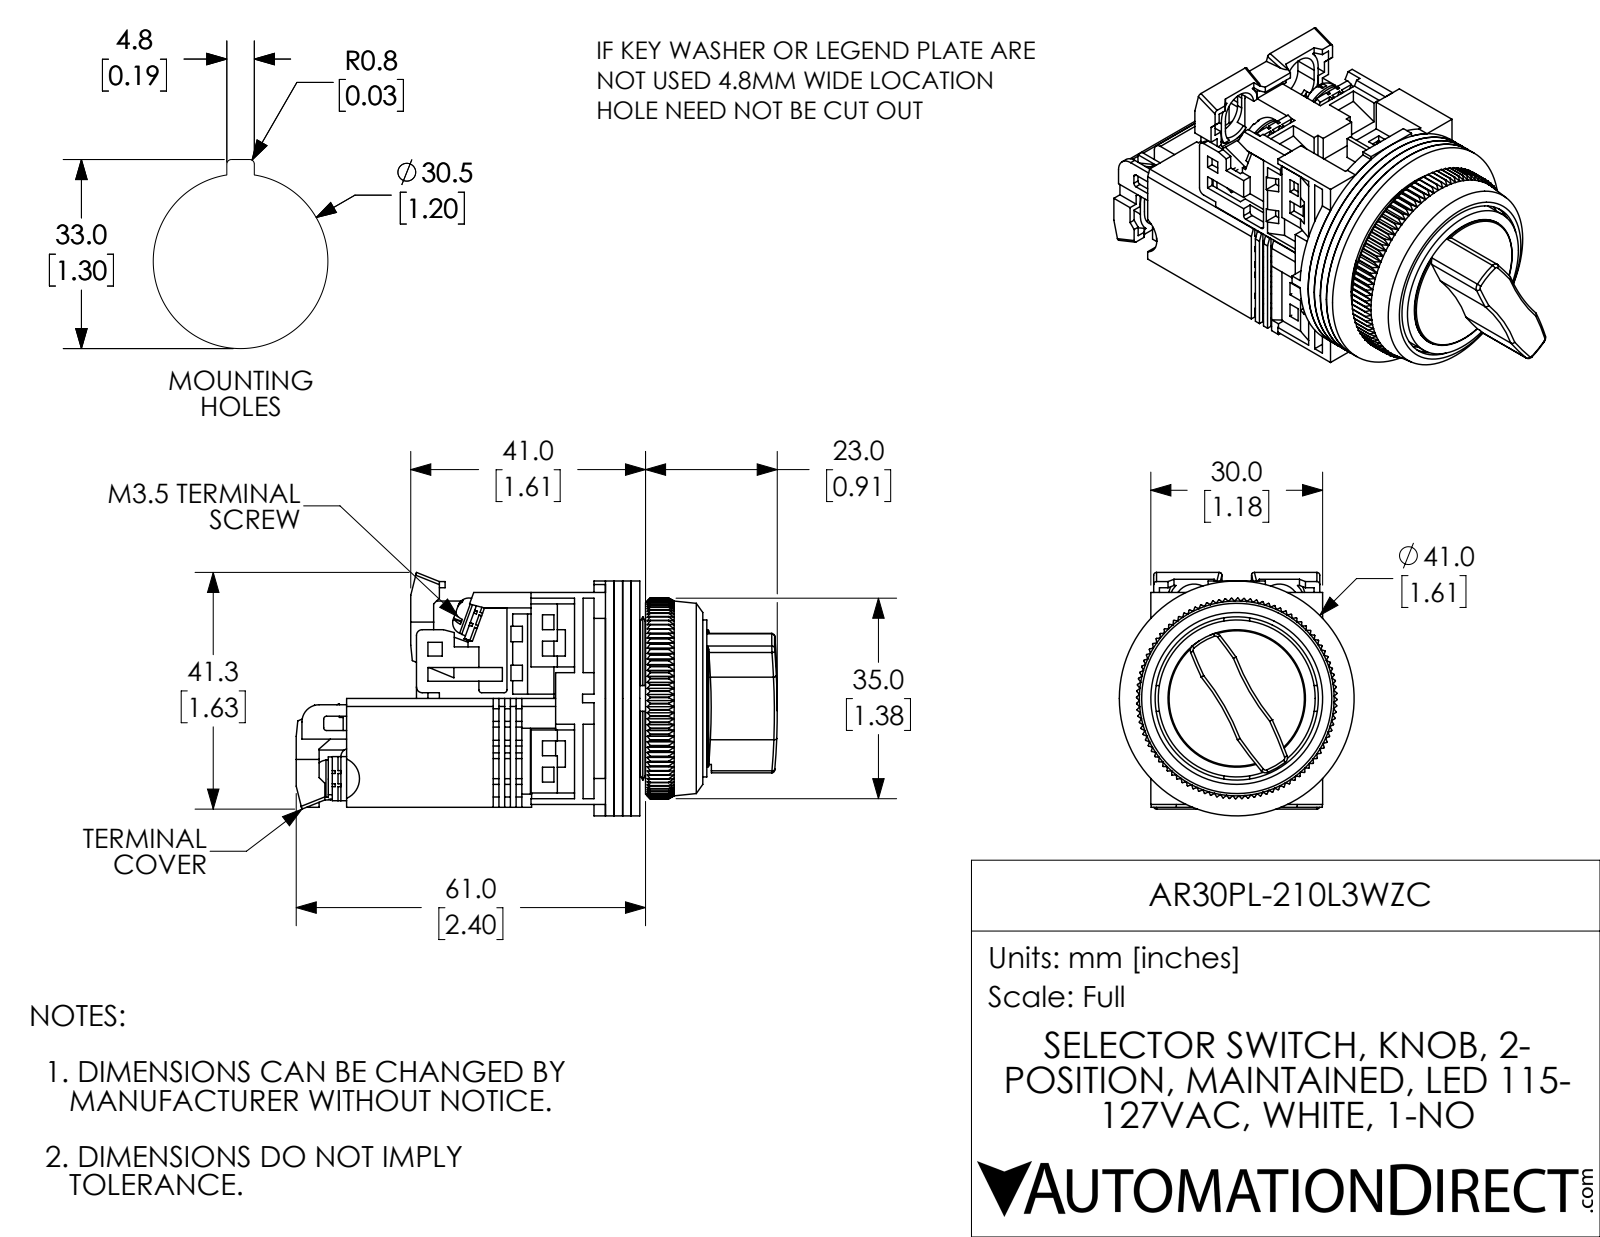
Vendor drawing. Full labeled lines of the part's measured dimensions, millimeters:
Part name (STEP PRODUCT): AR30PL-210L3WZC
STEP written by: SolidWorks 2017 (AUTOMOTIVE_DESIGN)
Units: millimetres
Bodies: 27 solids, 2357 faces (1706 planar, 321 cylindrical, 330 other)
Overall size (bounding box): 84 × 42.5 × 41
Volume: 49 180 mm³ · Surface area: 40 890 mm²
Round holes (diameter × count): ⌀3.5 ×6, ⌀3.6 ×4, ⌀3 ×3, ⌀12 ×1, ⌀18 ×1, ⌀19.5 ×1, ⌀21 ×1, ⌀28.5 ×1, ⌀30 ×1, ⌀31.8 ×1
Round bosses / shafts (diameter × count): ⌀6.6 ×4, ⌀3.5 ×2, ⌀1.6 ×2, ⌀41 ×1, ⌀29.2 ×1, ⌀27.4 ×1, ⌀24 ×1, ⌀22.5 ×1
Partial cylindrical surfaces — rounded edges, fillets, slot ends (radius × count): R1.5 ×17, R0.5 ×13, R1 ×6, R3.5 ×4, R4.5 ×4, R3 ×2, R40 ×2, R75 ×2
Main face-to-face distances: 1.5, 3, 4.5, 2, 1, 19, 20, 5, 6.5, 36
Hole centre spacings: 14.7, 7.5, 15.8, 0.5, 7.7, 14.8, 14.8, 15.4
